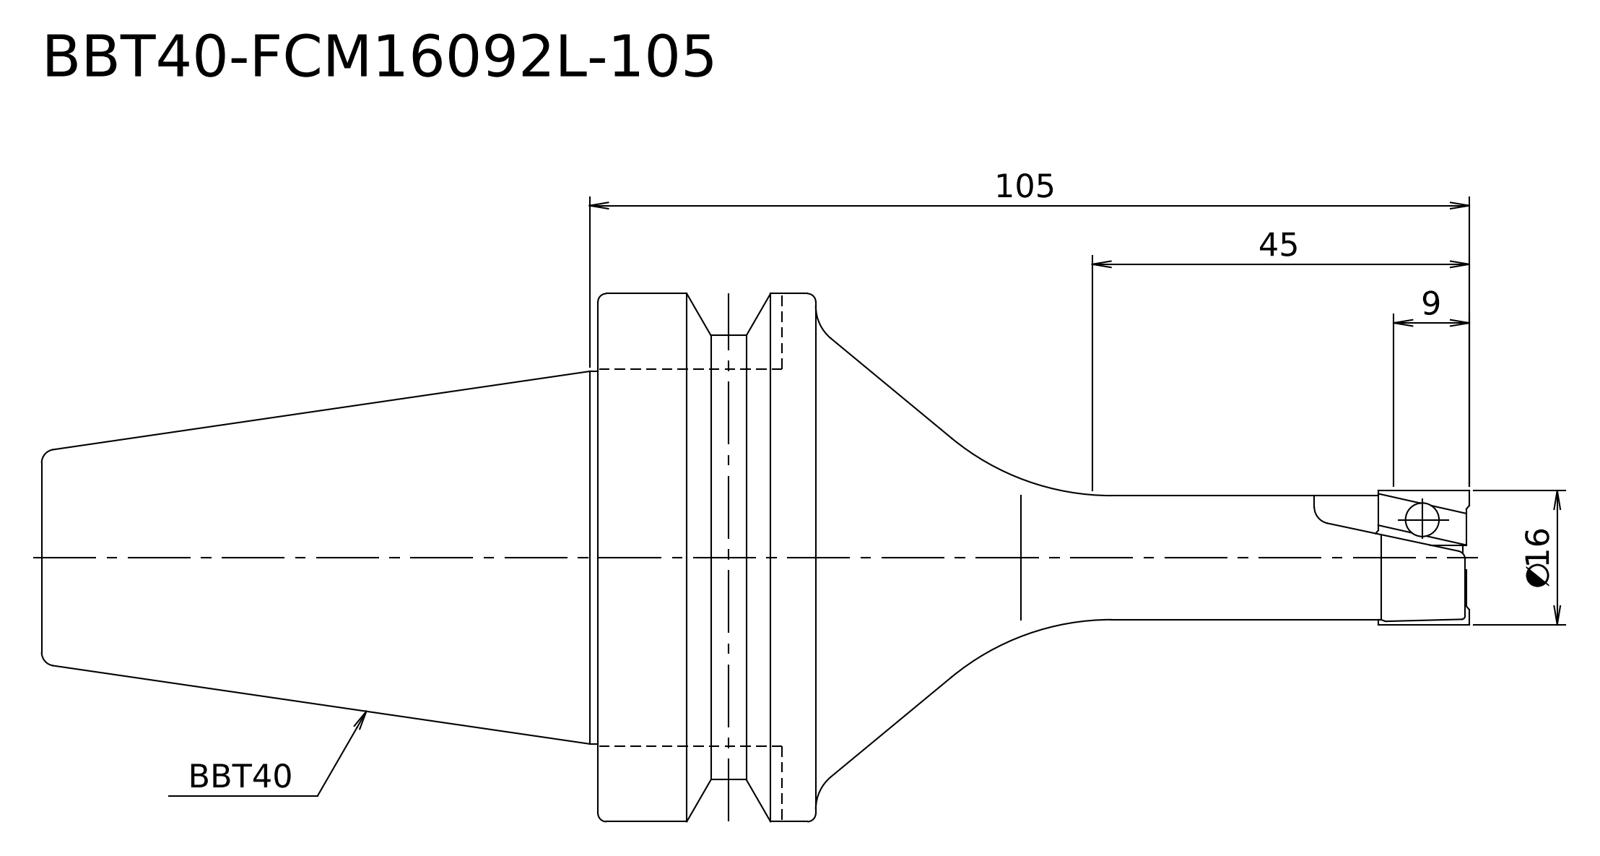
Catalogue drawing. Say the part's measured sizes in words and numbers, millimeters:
Its 3-D file was written by "Kubotek KeyCreator V8.5.1 (14335) (CONFIG_CONTROL_DESIGN)". It is 1 solid with 17 faces: 4 planar, 6 cylindrical and 7 other. Overall it measures 170.4 by 63 by 63 millimeters. Its volume is 178 592 cubic millimeters and its surface area 22 454 square millimeters. Round bosses or shafts: 1 of diameter 63, 1 of diameter 53, 1 of diameter 44.45, 1 of diameter 16, 1 of diameter 14.8. The main face-to-face distances are 66.4, 26, 92.4, 78, 104, 170.4.
